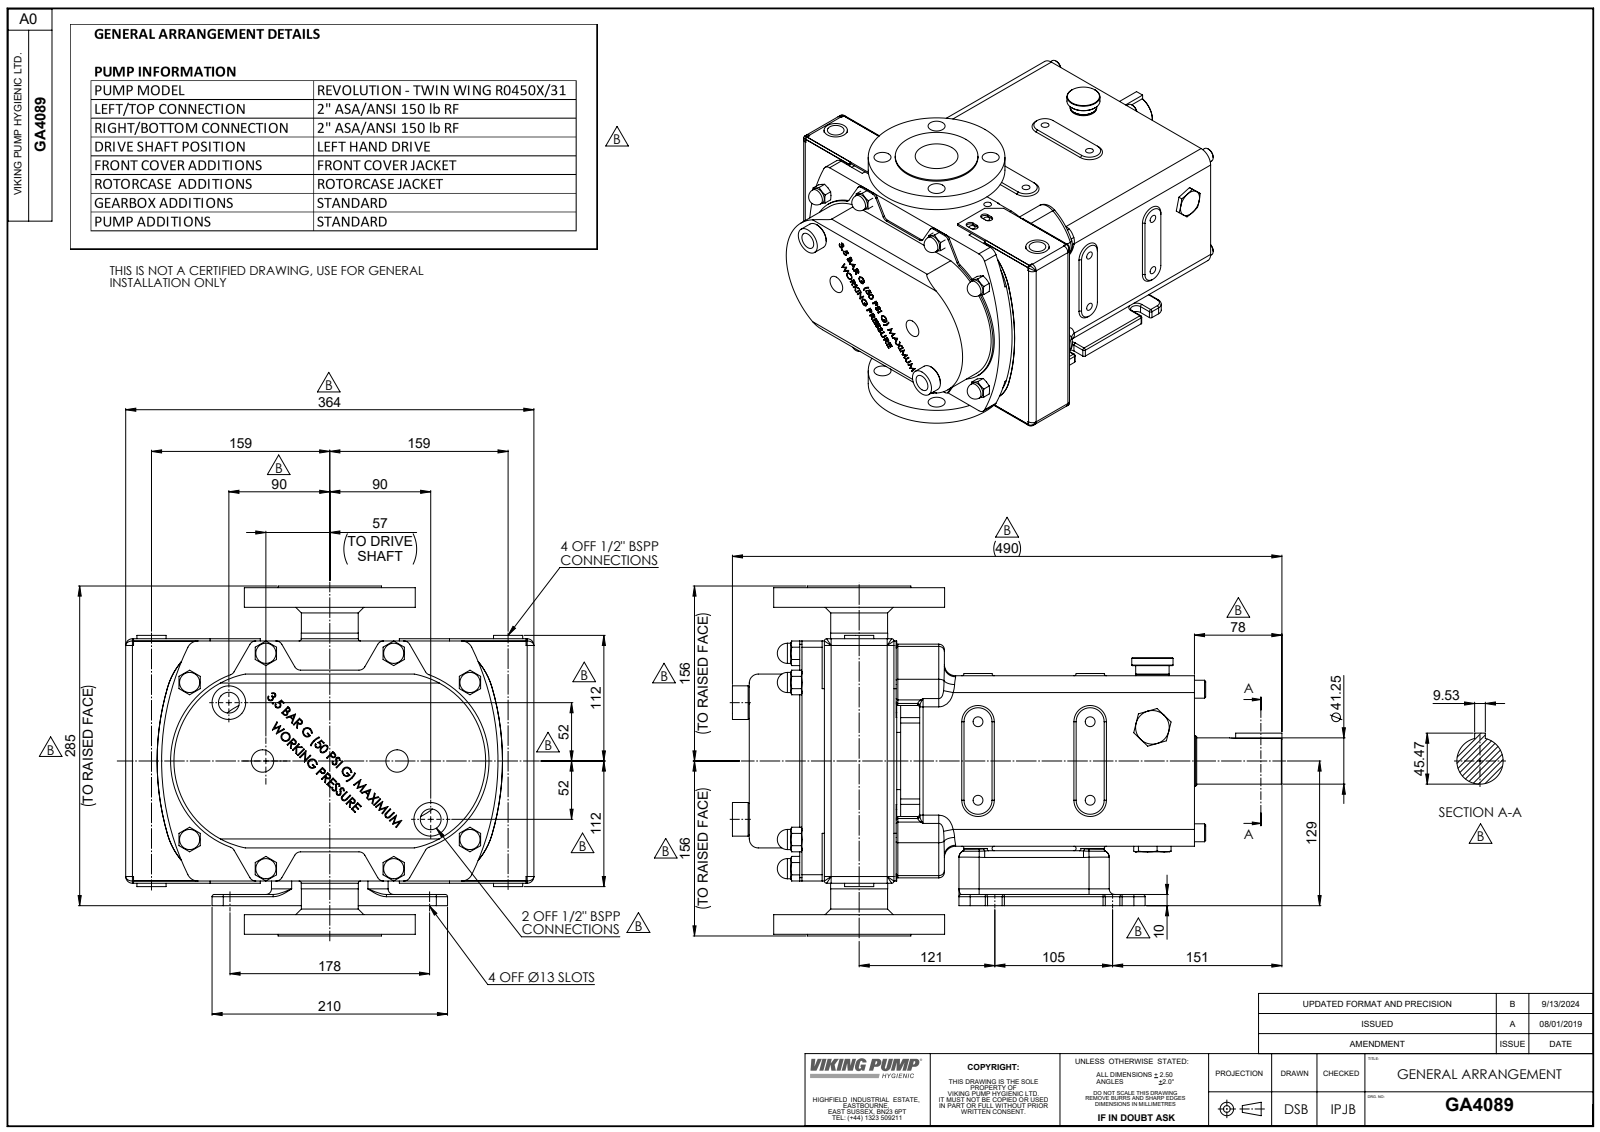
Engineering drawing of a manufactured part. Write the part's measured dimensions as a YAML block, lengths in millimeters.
part_name: "Copy of R0450 CPP V LHD^GA4089; GA4089; Copy of Size 4 Bolt on Jacket RC^GA4089; Copy of Frame 4 Bolt on Jacket^GA4089 (+1 more)"
step_written_by: "SolidWorks 2023 (AUTOMOTIVE_DESIGN)"
units: millimeters
bodies: {solids: 12, faces: 1806, planar: 775, cylindrical: 479, other: 552}
overall_size: [490, 364, 312]
volume: 17750000
surface_area: 1191000
round_holes:
  - {diameter: 8.8, count: 8}
  - {diameter: 19, count: 6}
  - {diameter: 6.8, count: 4}
  - {diameter: 15, count: 4}
  - {diameter: 18.6, count: 4}
  - {diameter: 8.6, count: 2}
  - {diameter: 26.2, count: 2}
  - {diameter: 33.8, count: 1}
  - {diameter: 47.7, count: 1}
round_bosses_or_shafts:
  - {diameter: 18, count: 8}
  - {diameter: 16, count: 6}
  - {diameter: 30, count: 4}
  - {diameter: 26, count: 3}
  - {diameter: 152.4, count: 1}
  - {diameter: 92.2, count: 1}
  - {diameter: 51, count: 1}
  - {diameter: 50.9, count: 1}
partial_cylinders:
  - {radius: 2, count: 42}
  - {radius: 10, count: 30}
  - {radius: 6, count: 28}
  - {radius: 5, count: 21}
  - {radius: 4, count: 8}
  - {radius: 4.5, count: 8}
  - {radius: 5.9, count: 8}
  - {radius: 15, count: 8}
face_to_face_distances: [2, 47, 152, 31, 183, 22, 84.5, 3, 266, 10]
hole_center_spacings: [60.3, 70, 85.28, 85.38, 100, 120.6, 122.07, 123.93]
